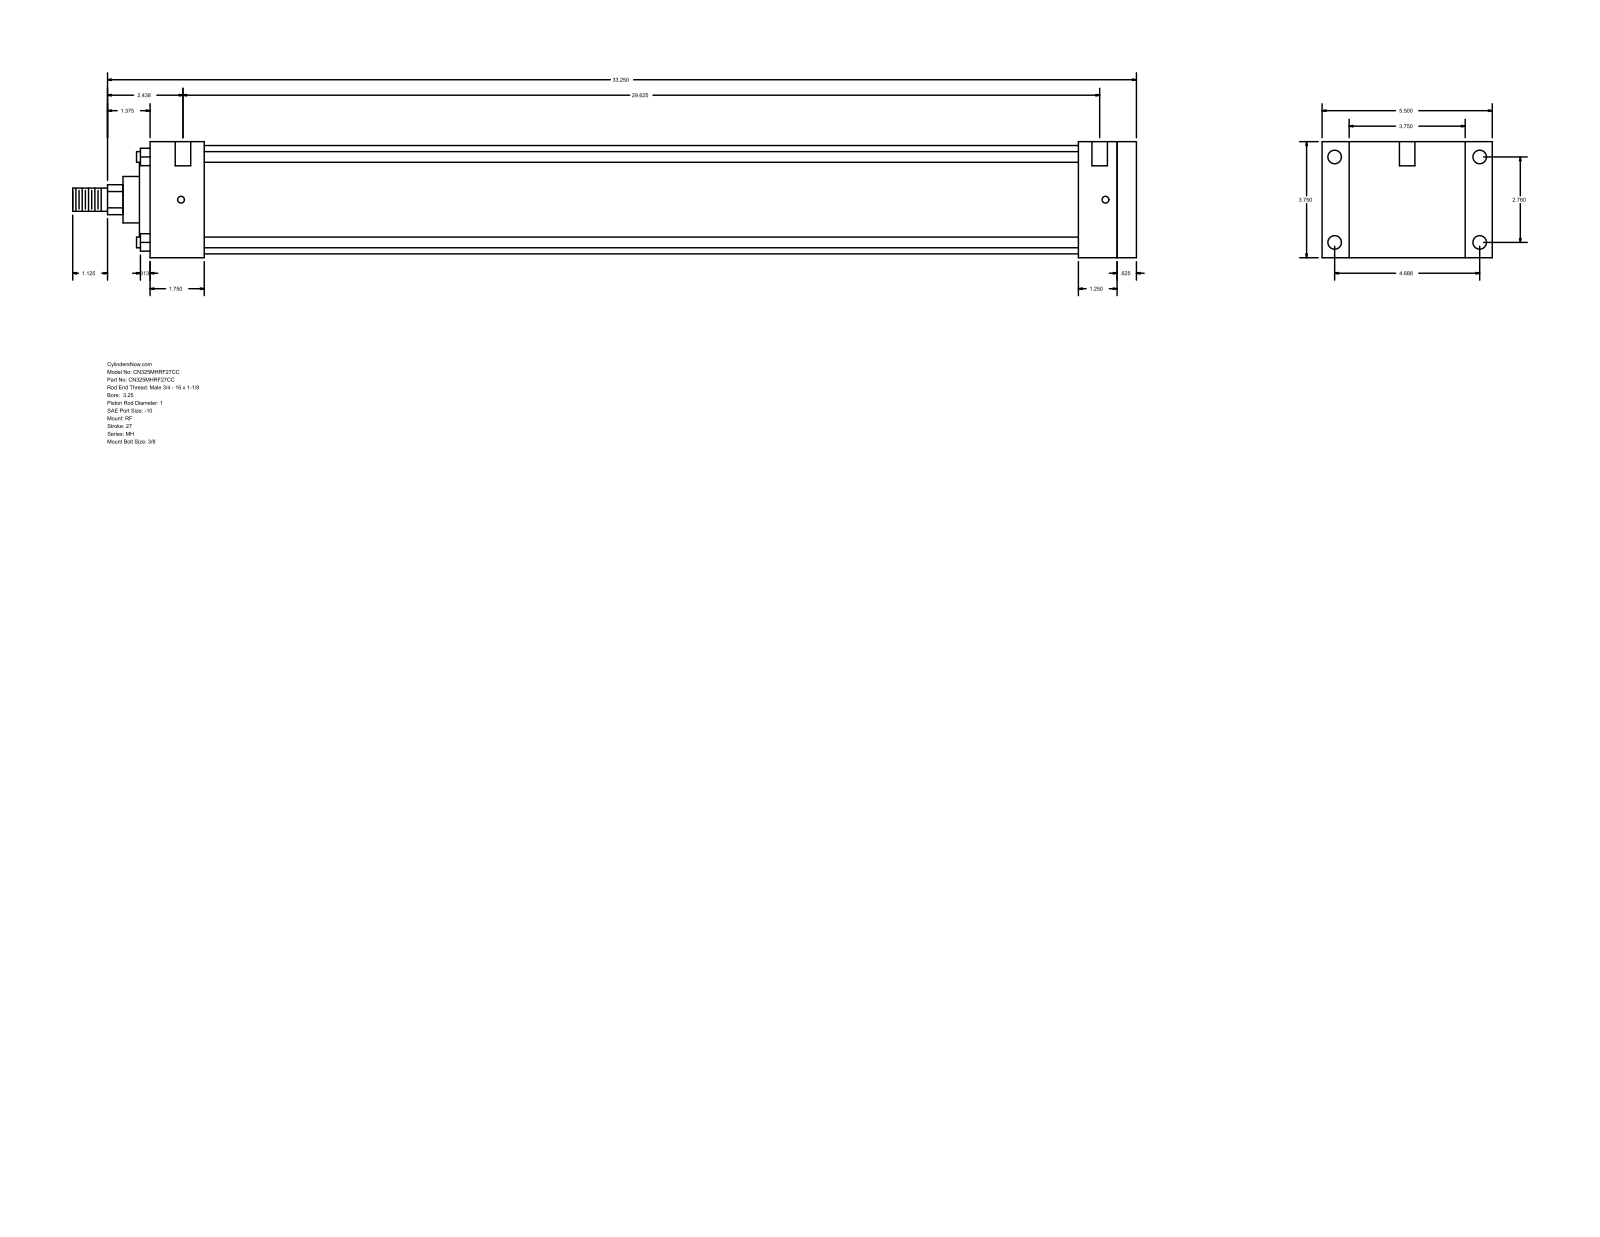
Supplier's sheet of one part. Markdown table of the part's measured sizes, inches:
| quantity | value |
| --- | --- |
| part name | MH_RF__0325_1 |
| STEP written by | GSSL Pune (CONFIG_CONTROL_DESIGN) |
| units | inches |
| bodies | 0 solids, 94 faces (65 planar, 29 cylindrical, 0 other) |
| overall size | 34.375 × 5.5 × 3.75 |
| round holes (diameter × count) | 0.219 × 4, 0.438 × 4, 0.5 × 2 |
| round bosses / shafts (diameter × count) | 0.345 × 4, 3.5 × 1, 2.375 × 1, 1.5 × 1, 1 × 1, 0.75 × 1 |
| partial cylindrical surfaces (radius × count) | 0.484 × 1 |
| main face-to-face distances | 3.75, 31.875, 31.25, 0.625, 0.875, 4.625, 1.75, 29.5, 30.125, 30 |
| hole center spacings | 2.76, 4.687, 5.439, 29.875, 0.062, 0.187, 29.625, 29.687 |
